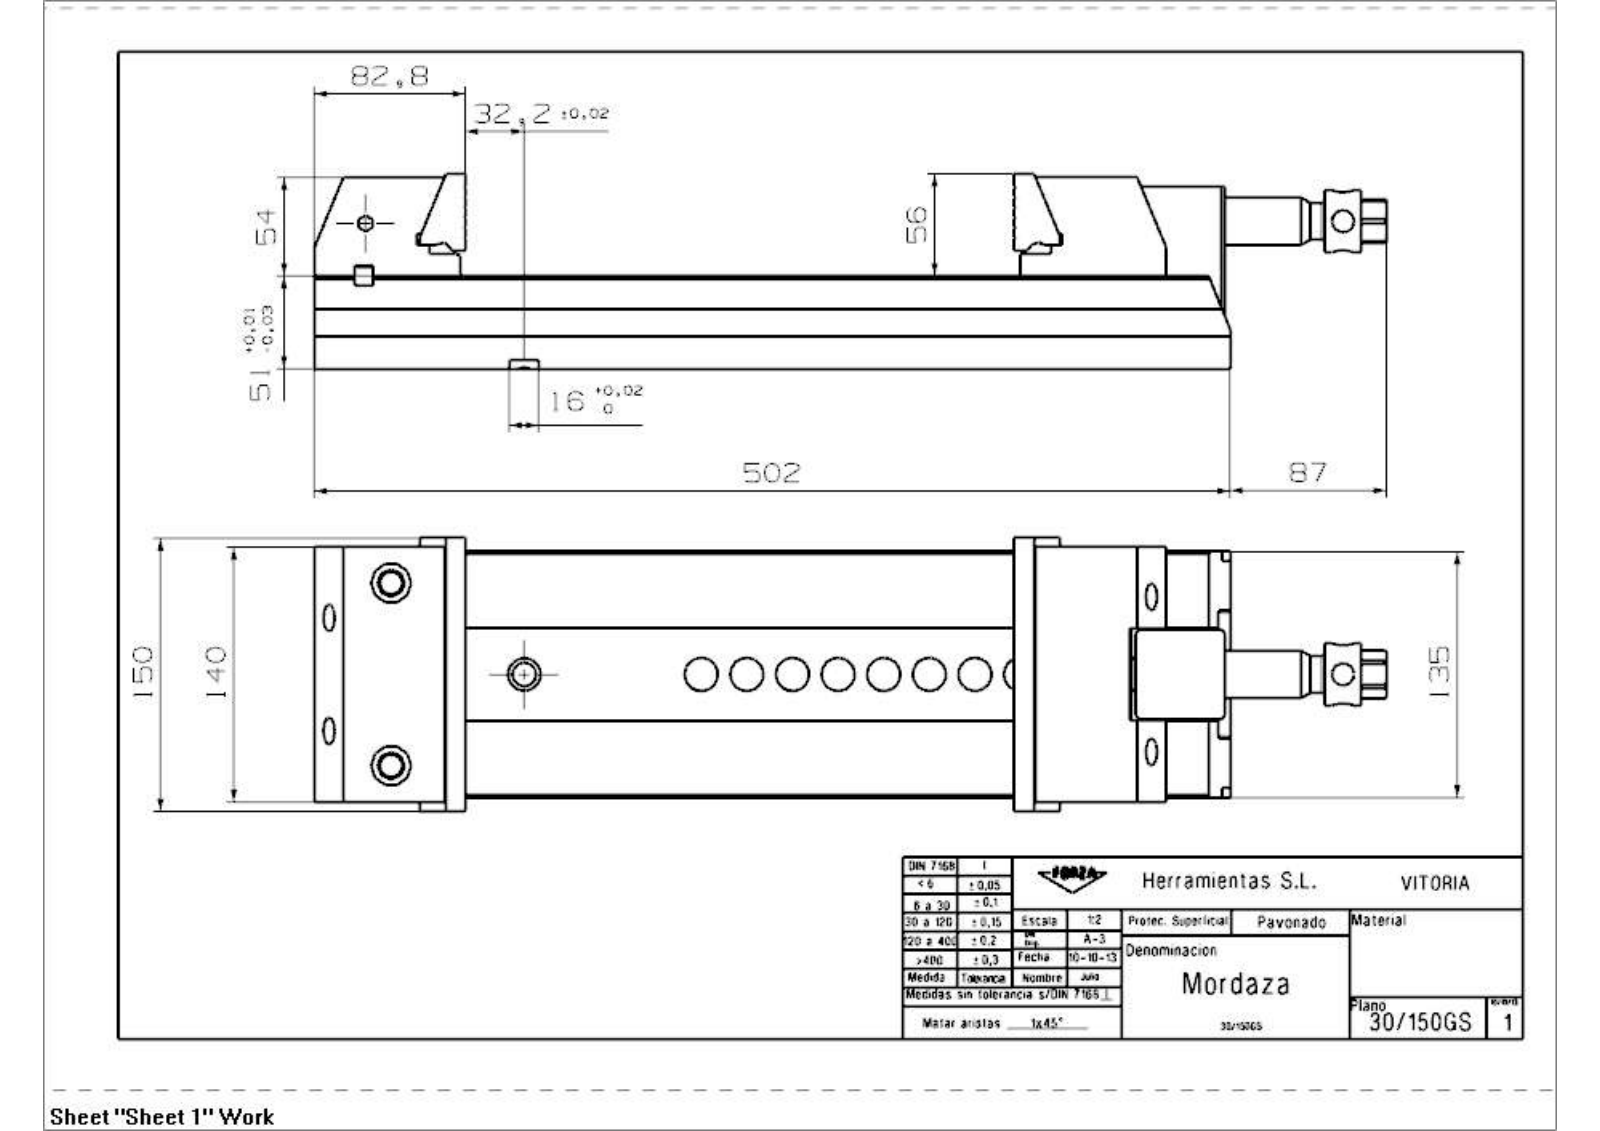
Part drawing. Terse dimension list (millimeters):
name: 30_150GS_Mordaza
written by: SIEMENS PLM Software NX 7.5 (CONFIG_CONTROL_DESIGN)
unit: mm
bodies: 12 solids, 450 faces (296 planar, 98 cylindrical, 56 other)
size: 587.76 × 150 × 107
volume: 3 642 000 mm³; area: 499 050 mm²
holes: 6× ⌀13, 6× ⌀15, 5× ⌀5.19, 4× ⌀6.99, 4× ⌀8.5, 4× ⌀8.78, 4× ⌀10.58, 4× ⌀19, 2× ⌀9.7, 2× ⌀10, 2× ⌀12, 2× ⌀12.38
bosses: 1× ⌀34, 1× ⌀33.8, 1× ⌀26, 1× ⌀20, 1× ⌀16.5
rounds: 4× R1.5, 4× R8, 4× R20, 2× R1.6, 2× R5.5, 2× R6, 1× R4, 1× R9
face distances: 51, 19.3, 31.7, 5.5, 105, 49.4, 1.6, 17.7, 135, 8
hole spacings: 11.5, 67.27, 73.5, 85, 95.17, 95.18, 11.54, 11.61
